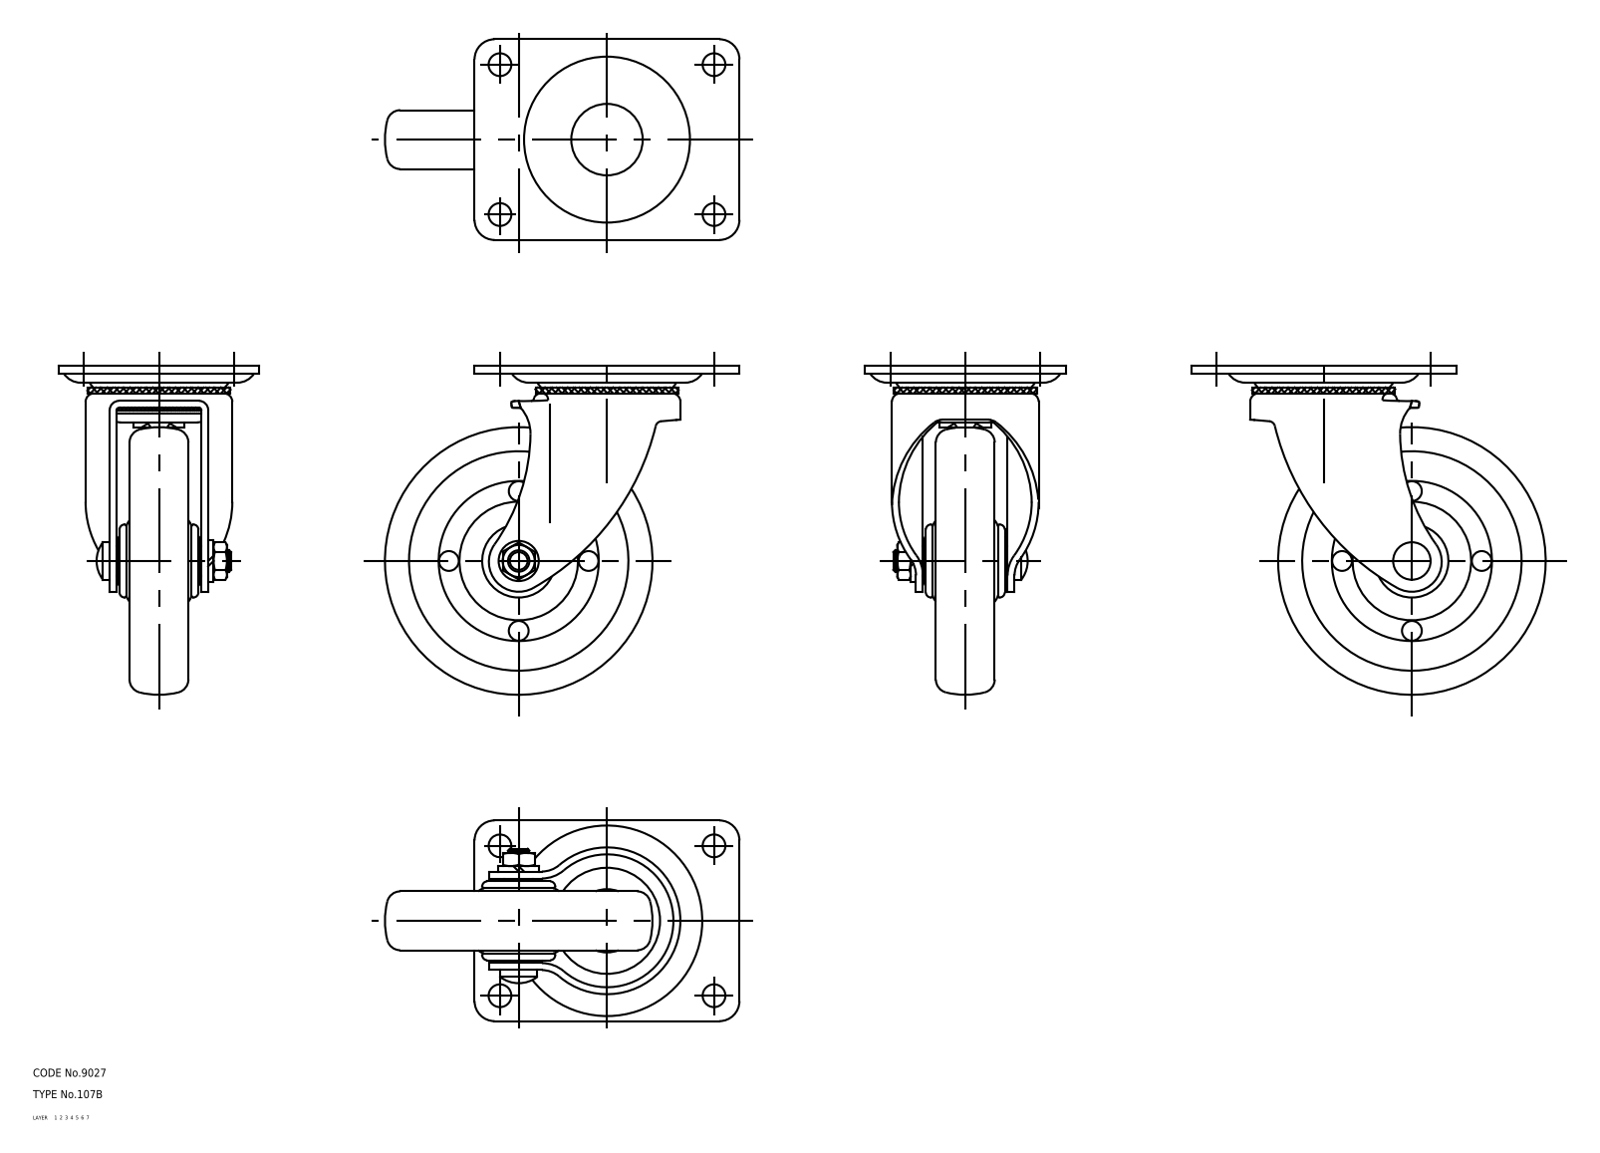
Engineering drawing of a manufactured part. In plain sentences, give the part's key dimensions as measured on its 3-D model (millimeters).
The part is named "67127868; 67127881; 67127894; 67127907 (+1 more)". Its 3-D file was written by "CADfix (AUTOMOTIVE_DESIGN)". It is 5 solids with 247 faces: 0 planar, 0 cylindrical and 247 other. Overall it measures 132.5 by 123 by 75 millimeters. Its volume is 219 304 cubic millimeters and its surface area 65 430 square millimeters.
